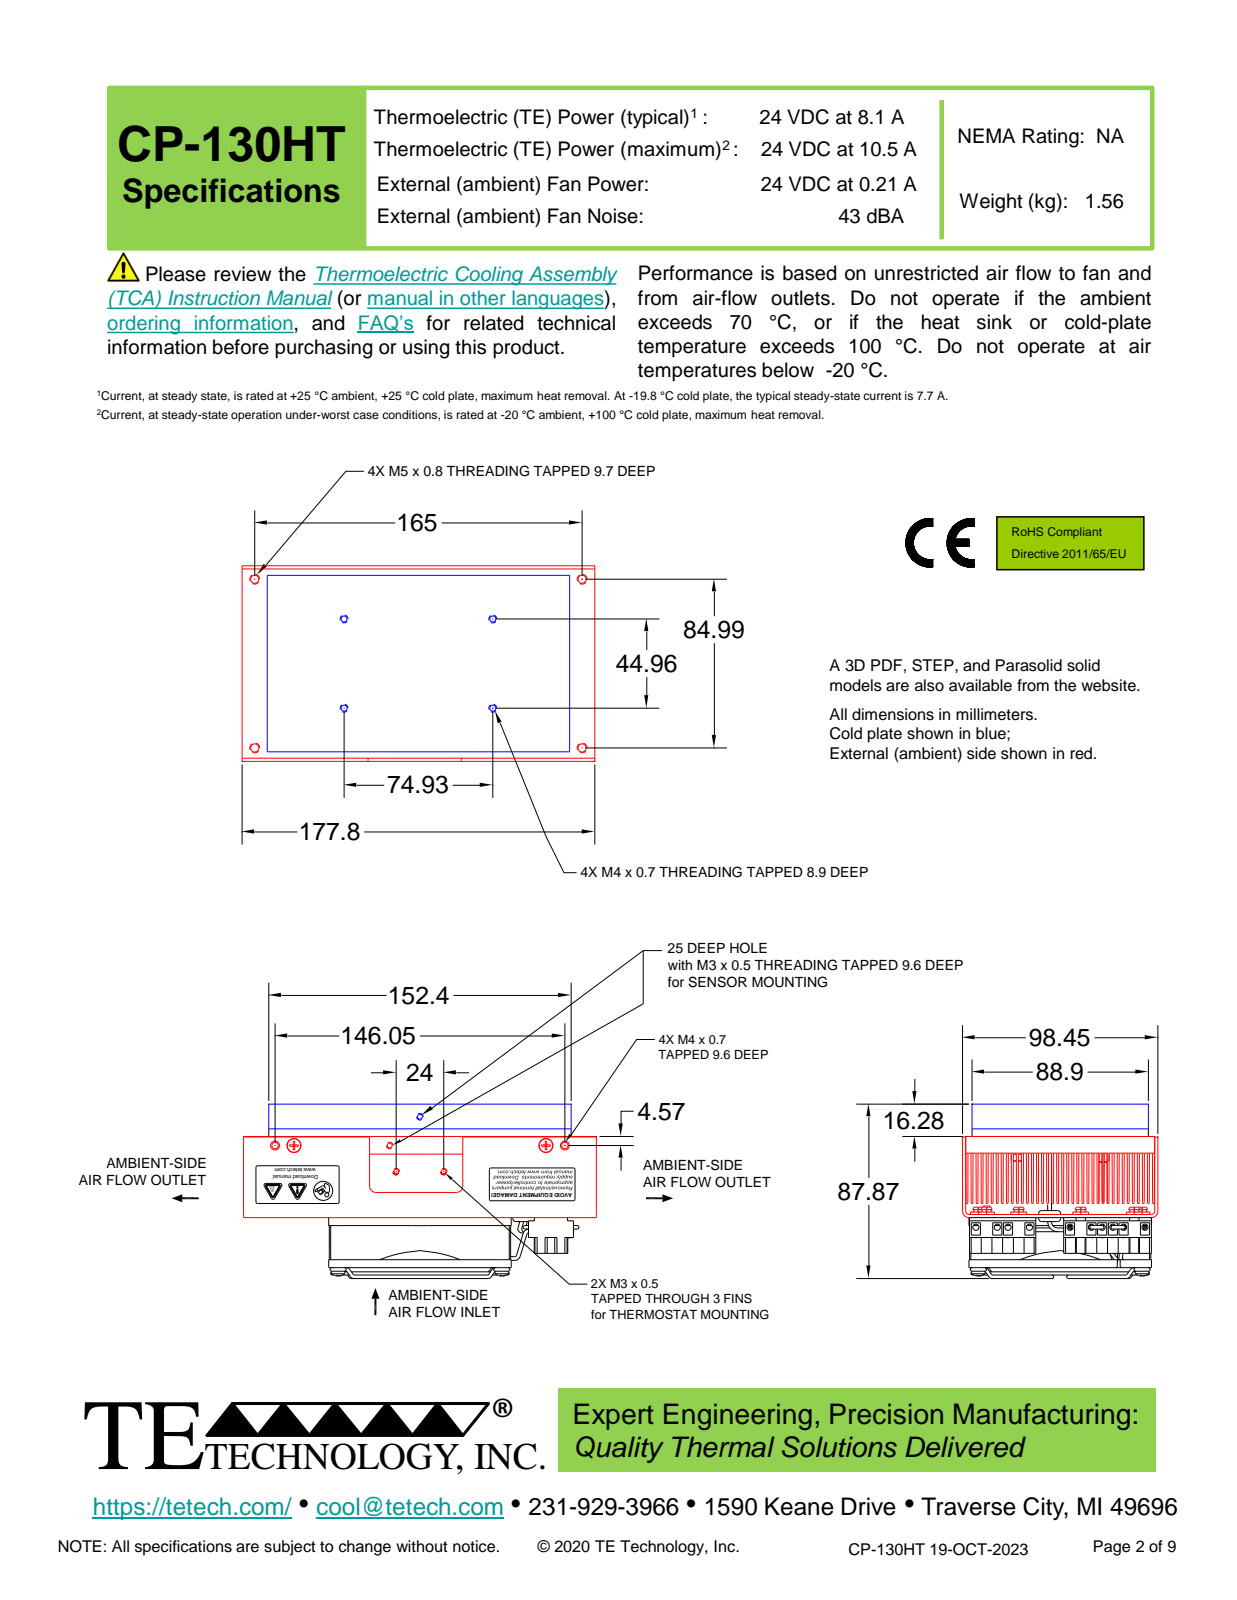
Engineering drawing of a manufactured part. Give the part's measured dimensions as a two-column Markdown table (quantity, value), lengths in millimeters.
| quantity | value |
| --- | --- |
| part name | cold plate CP-130HT; 7355 gasket; 7356 heat sink; 6-32socket-head x .75 (+8 more) |
| STEP written by | Alibre (AUTOMOTIVE_DESIGN) |
| units | millimeters |
| bodies | 129 solids, 3522 faces (1532 planar, 536 cylindrical, 1454 other) |
| overall size | 177.8 × 98.58 × 87.87 |
| volume | 623 201 mm³ |
| surface area | 558 456 mm² |
| round holes (diameter × count) | 4 × 12, 2.64 × 10, 2.65 × 8, 5.56 × 8, 3.1 × 6, 3.24 × 6, 4.17 × 6, 4.22 × 6, 4.27 × 6, 4.83 × 6, 5.59 × 6, 5.74 × 6 |
| round bosses / shafts (diameter × count) | 3.51 × 18, 1.42 × 18, 1.83 × 10, 1.8 × 9, 6.86 × 8, 6.34 × 8, 1.8 × 8, 11.18 × 6 |
| partial cylindrical surfaces (radius × count) | 1 × 49, 0.2 × 34, 0.25 × 16, 3 × 12, 0.5 × 10, 0.7 × 4, 2.35 × 4, 3.75 × 4 |
| main face-to-face distances | 3.84, 12.44, 16.28, 1.61, 96.85, 57.17, 44.73, 40.89, 24.66, 12.22 |
| hole center spacings | 68.58, 81.31, 16.2, 33.52, 68.76, 85.05, 111.53, 164.21 |
